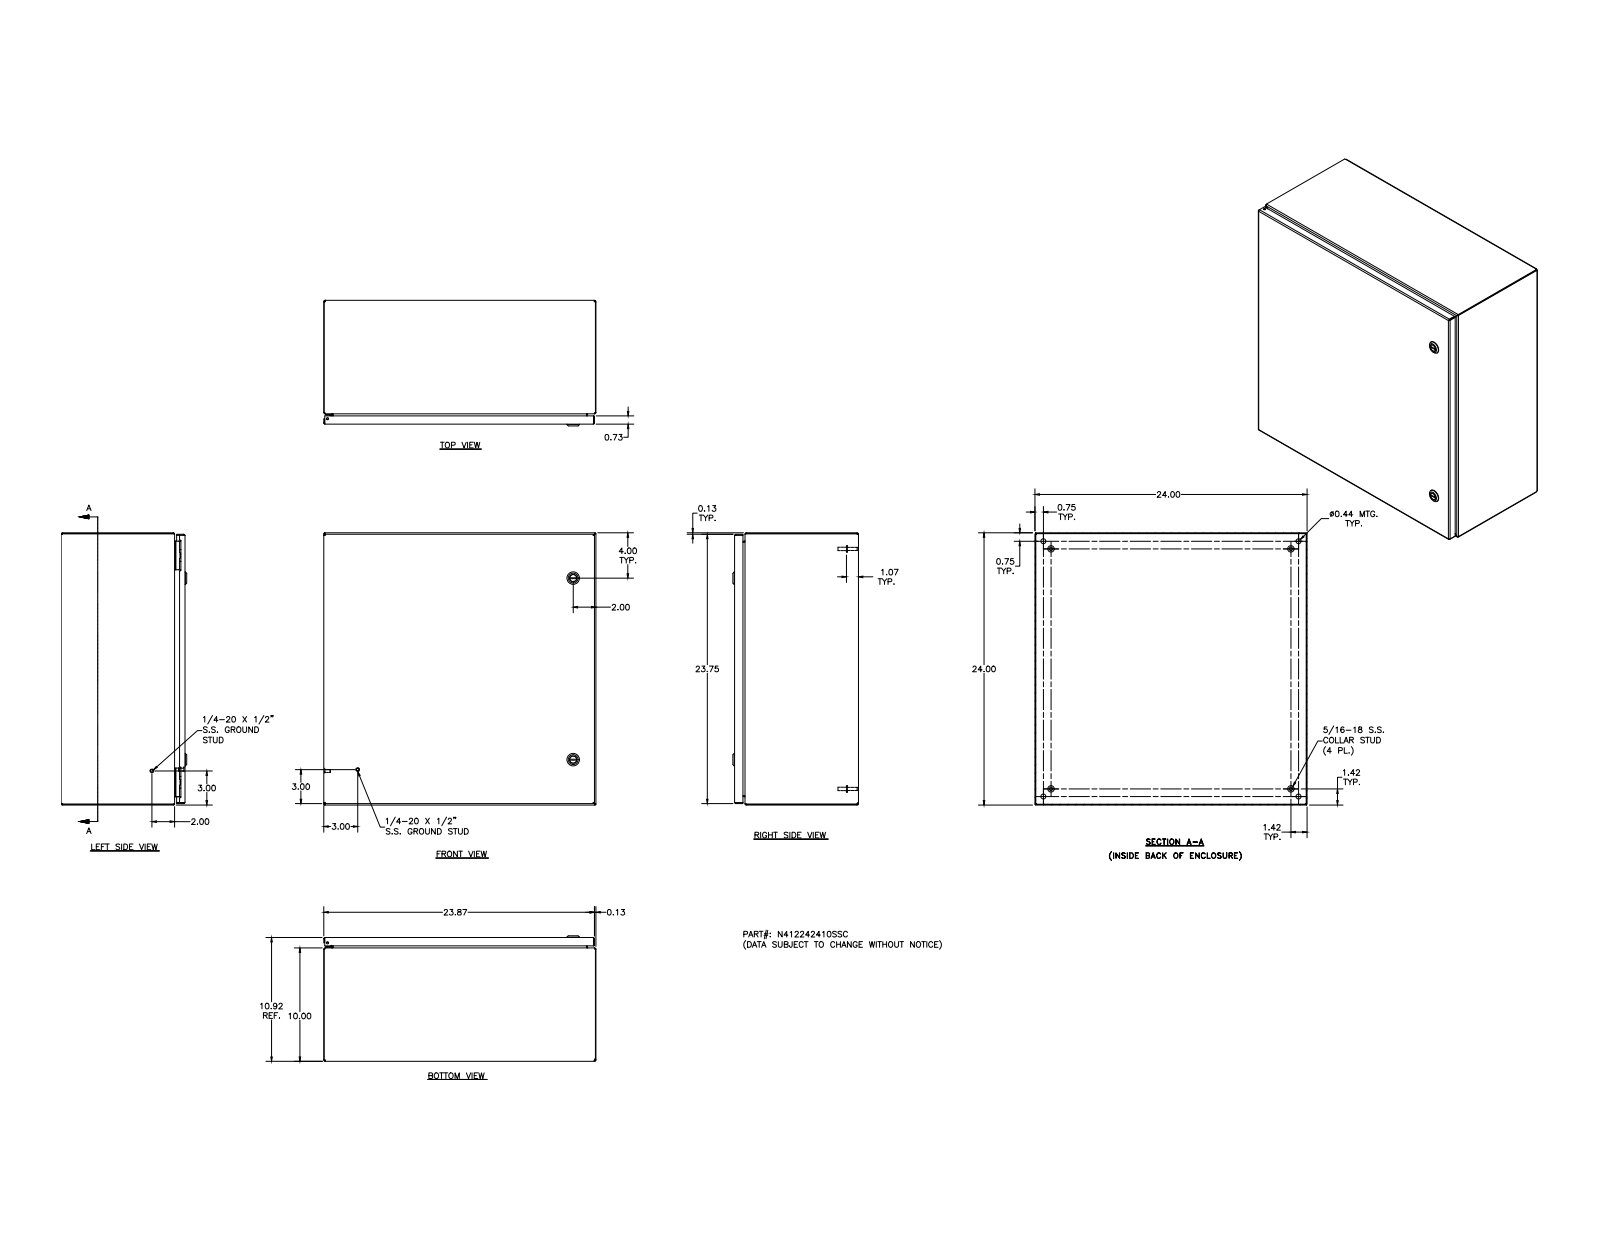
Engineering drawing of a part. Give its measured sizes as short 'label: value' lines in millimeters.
name: N412242410SSC; N412242410SSCBKP; 388151; N4122424SSCLID (+8 more)
written by: Autodesk Inventor 2011 (AUTOMOTIVE_DESIGN)
unit: mm
bodies: 42 solids, 1682 faces (706 planar, 600 cylindrical, 376 other)
size: 609.6 × 609.6 × 281.3
volume: 2 804 000 mm³; area: 2 995 000 mm²
holes: 5× ⌀4.8, 4× ⌀2.4, 4× ⌀3.9, 4× ⌀4.2, 4× ⌀4.4, 4× ⌀11.1, 2× ⌀4, 2× ⌀5, 2× ⌀8, 2× ⌀10, 2× ⌀10.2, 2× ⌀16.1
bosses: 10× ⌀6.4, 4× ⌀14.3, 4× ⌀9.1, 4× ⌀8.1, 4× ⌀7.6, 4× ⌀7, 4× ⌀6.5, 4× ⌀4.2
rounds: 30× R0.8, 26× R1.3, 20× R2.7, 18× R0.4, 15× R0.5, 14× R3.2, 8× R0.8, 8× R1.8
face distances: 1.9, 275.4, 607.7, 277.3, 273.5, 605.8, 609.6, 252.1, 23.3, 18.8
hole spacings: 508, 0.4, 16.8, 571.5, 580.9, 0.5, 12.7, 16.5
